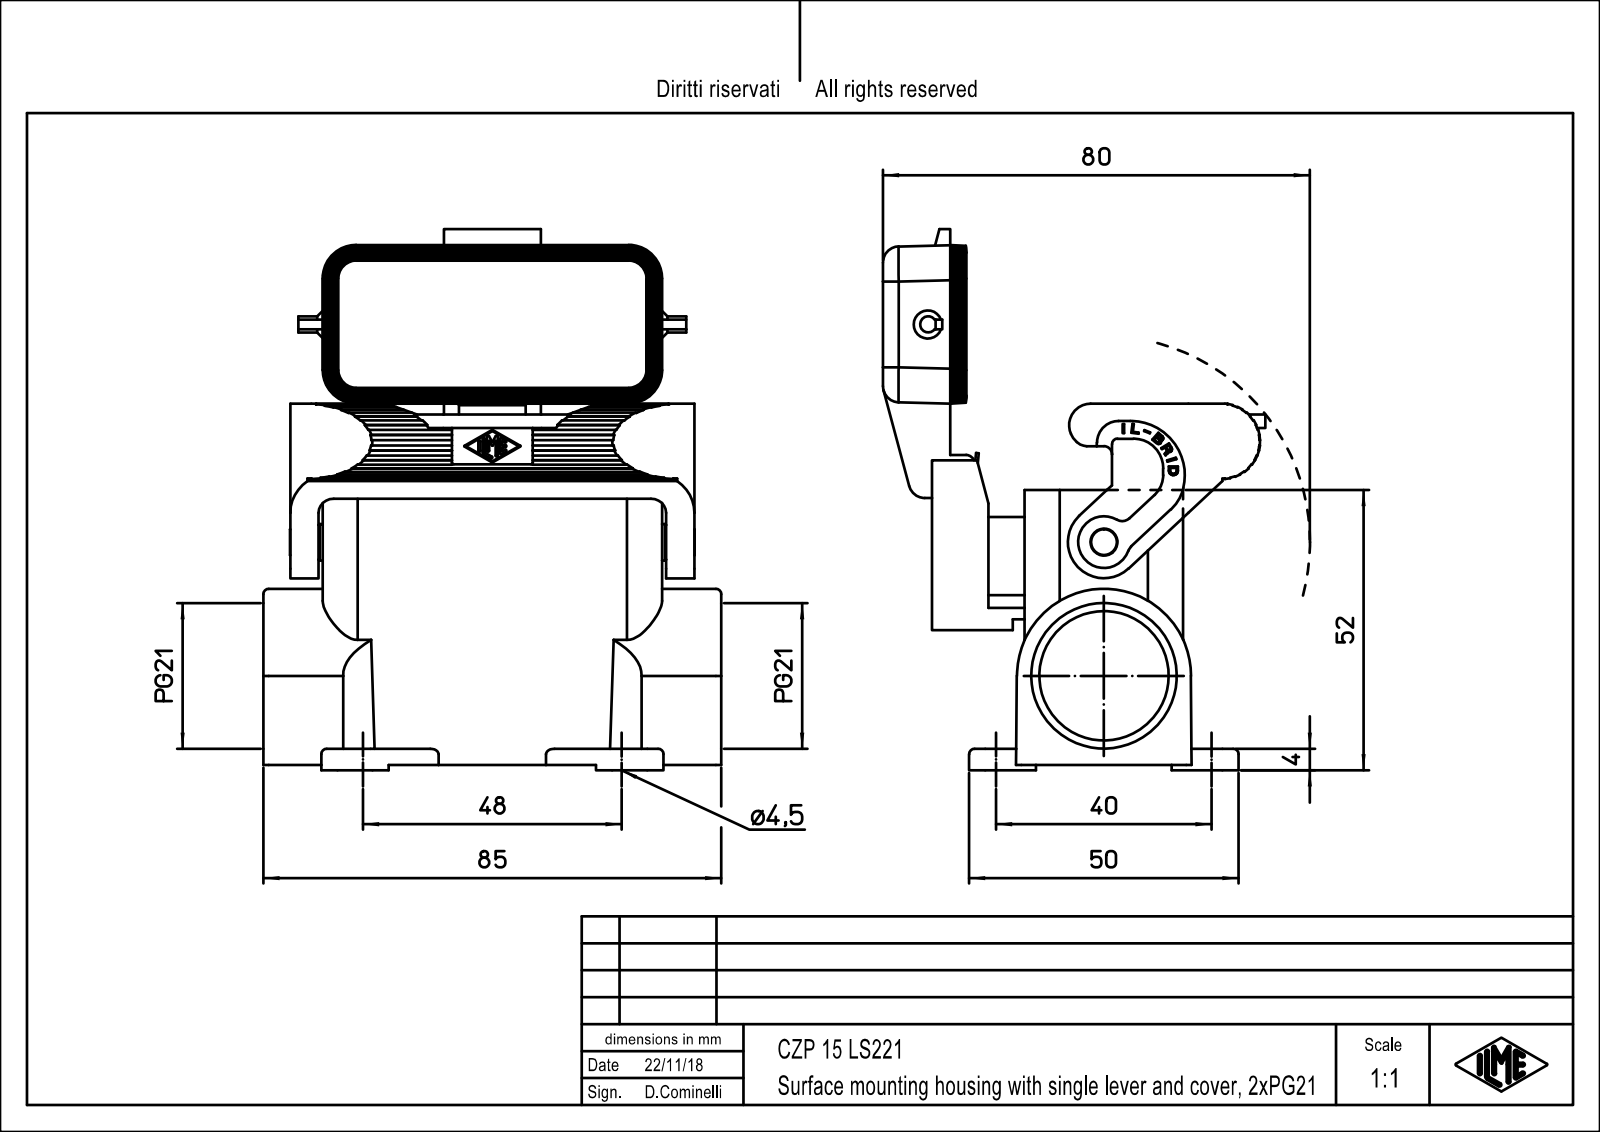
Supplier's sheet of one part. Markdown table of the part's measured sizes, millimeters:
| quantity | value |
| --- | --- |
| part name | CZP_15_LS221 |
| STEP written by | PTC Creo Elements/Direct Modeling 19.0E 27-Jun-2016 (C) Parametric Technology GmbH (AUTOMOTIVE_DESIGN) |
| units | millimeters |
| bodies | 1 solid, 538 faces (307 planar, 197 cylindrical, 34 other) |
| overall size | 100.4 × 85 × 71 |
| volume | 71 247 mm³ |
| surface area | 47 060 mm² |
| round holes (diameter × count) | 3 × 4, 4.5 × 4, 5 × 1, 24 × 1, 27 × 1 |
| round bosses / shafts (diameter × count) | 7 × 1, 6.8 × 1, 4.8 × 1, 3 × 1 |
| partial cylindrical surfaces (radius × count) | 0.2 × 15, 3 × 14, 1 × 13, 6.5 × 8, 3.5 × 4, 3.5 × 4, 6 × 4, 0.1 × 3 |
| main face-to-face distances | 2.6, 26.8, 24.2, 29.4, 2, 57.5, 3, 26.9, 53.7, 51.1 |
| hole center spacings | 12.02, 28.01, 50.21, 56.22, 16, 40, 48, 49.5 |
